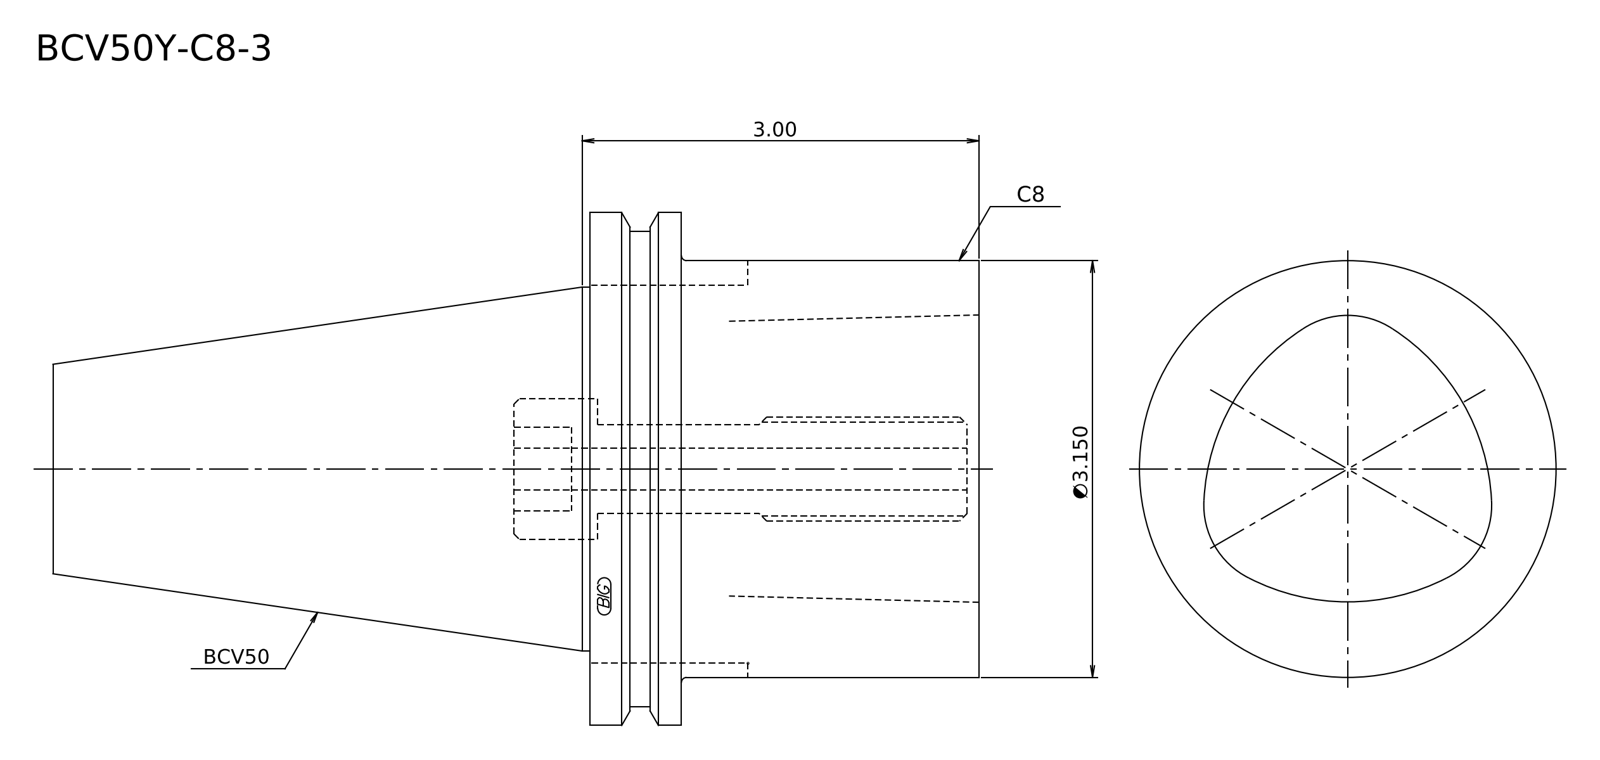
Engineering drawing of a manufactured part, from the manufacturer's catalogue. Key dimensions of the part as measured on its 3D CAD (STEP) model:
STEP written by: Kubotek KeyCreator 2011 V10.0.2 (22737) (automotive_design)
Units: millimetres
Bodies: 1 solid, 15 faces (6 planar, 5 cylindrical, 4 other)
Overall size (bounding box): 177.8 × 98.42 × 98.42
Volume: 668 752 mm³ · Surface area: 51 686 mm²
Round bosses / shafts (diameter × count): ⌀98.42 ×1, ⌀91.29 ×1, ⌀80 ×1, ⌀69.85 ×1
Main face-to-face distances: 74.7, 57.15, 17.55, 177.8, 120.65, 103.1, 67, 9.85, 7.7, 110.8
